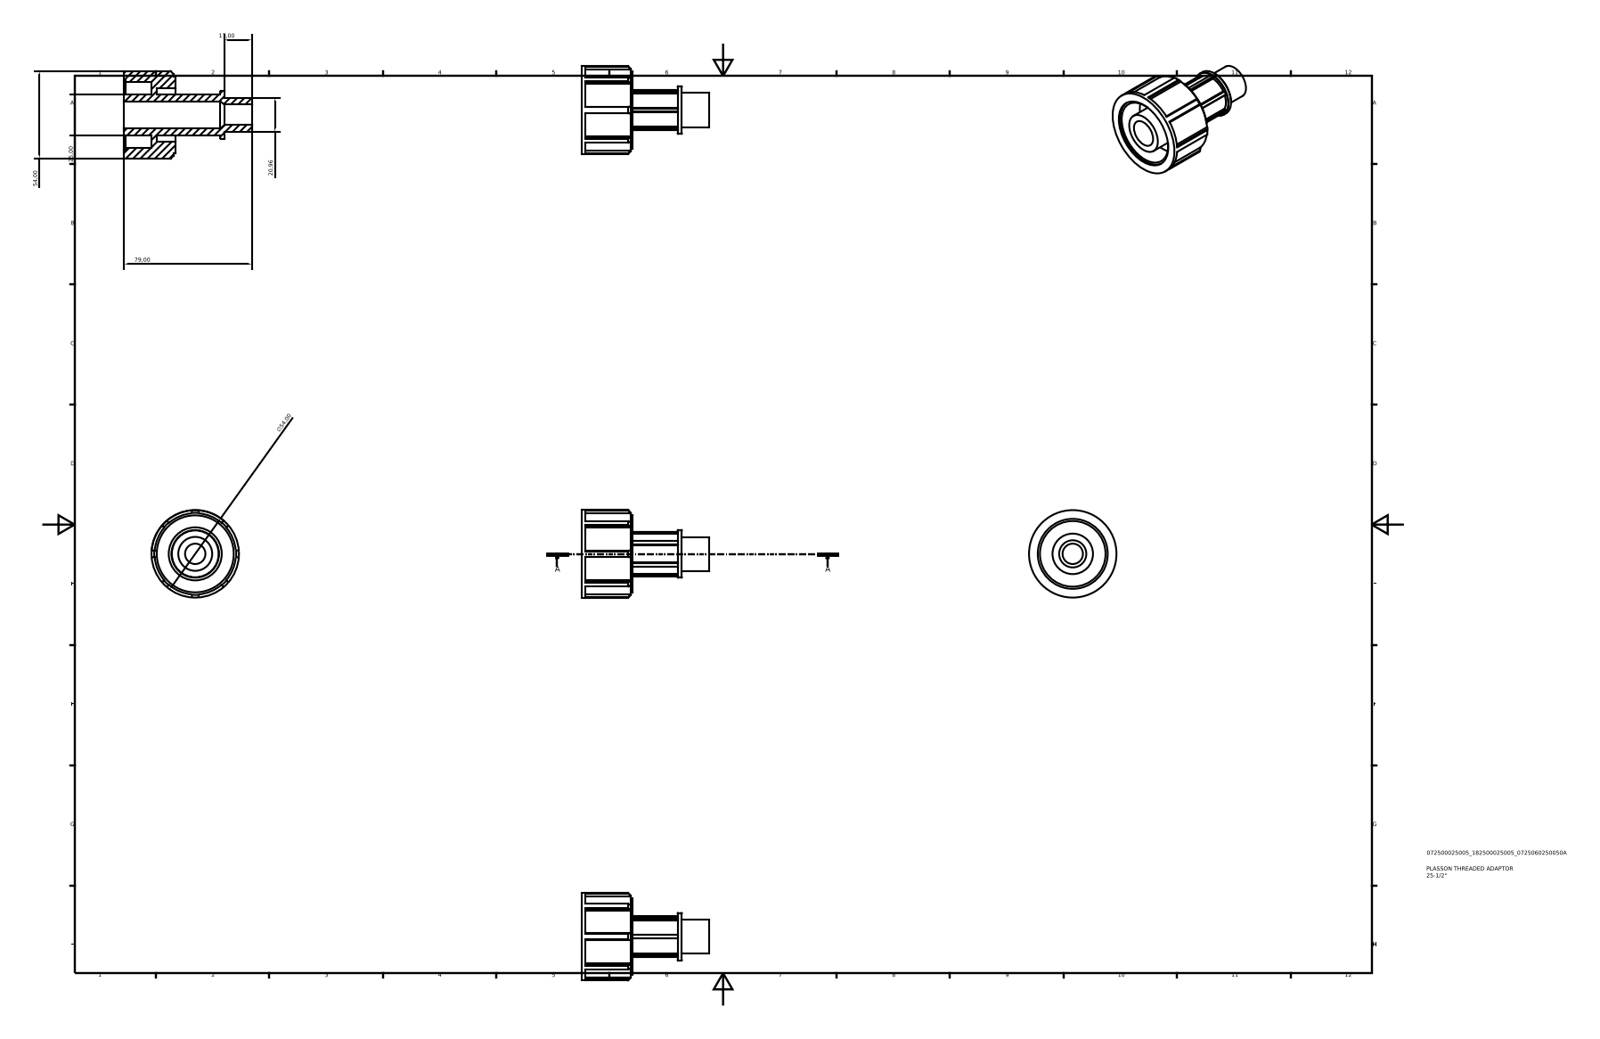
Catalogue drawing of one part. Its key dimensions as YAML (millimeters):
part_name: "072500025005_182500025005"
step_written_by: "Autodesk Inventor 2015 (AUTOMOTIVE_DESIGN)"
units: millimeters
bodies: {solids: 1, faces: 115, planar: 74, cylindrical: 30, other: 11}
overall_size: [79, 54, 54]
volume: 53384
surface_area: 23823
round_holes:
  - {diameter: 12.57, count: 1}
  - {diameter: 16.76, count: 1}
  - {diameter: 32.75, count: 1}
  - {diameter: 40.5, count: 1}
  - {diameter: 43.2, count: 1}
round_bosses_or_shafts:
  - {diameter: 54, count: 1}
  - {diameter: 47.52, count: 1}
  - {diameter: 29.34, count: 1}
  - {diameter: 25, count: 1}
  - {diameter: 20.95, count: 1}
partial_cylinders:
  - {radius: 13.75, count: 1}
  - {radius: 25.11, count: 1}
face_to_face_distances: [17, 31.6, 14.6, 62, 1.19, 30.41, 20.4, 3.4, 11.2, 4.2]
